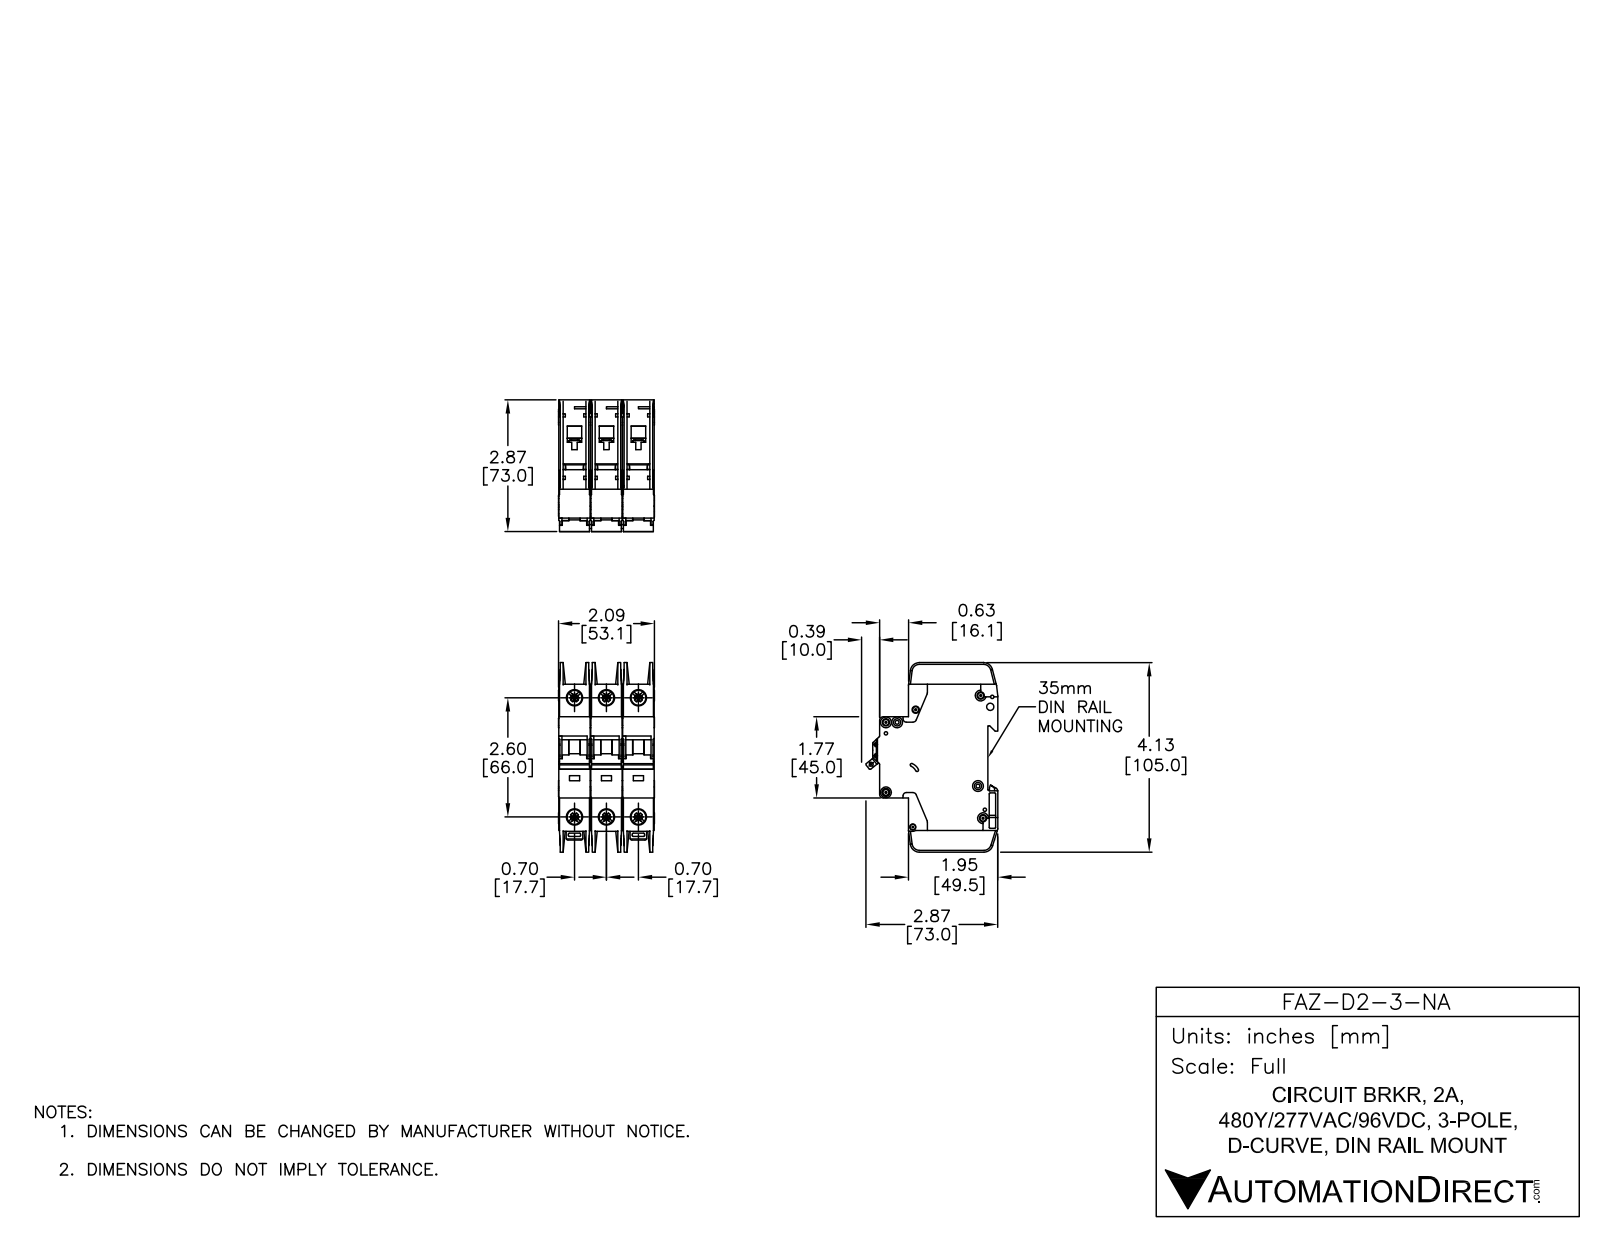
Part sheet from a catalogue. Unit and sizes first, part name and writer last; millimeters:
Units: millimetres
Overall size (bounding box): 105 × 73.04 × 53.1
Round holes (diameter × count): ⌀3.6 ×7, ⌀7.15 ×6, ⌀8.2 ×6, ⌀1.09 ×2, ⌀1.5 ×2, ⌀4 ×2, ⌀1.9 ×1, ⌀2.15 ×1, ⌀2.2 ×1, ⌀2.55 ×1, ⌀3.3 ×1, ⌀3.4 ×1
Round bosses / shafts (diameter × count): ⌀6 ×7, ⌀2.5 ×3
Partial cylindrical surfaces — rounded edges, fillets, slot ends (radius × count): R0.25 ×65, R0.5 ×30, R1 ×26, R2 ×14, R1.8 ×5, R5 ×5, R4 ×4, R0.2 ×2
Main face-to-face distances: 17.7, 35.4, 17.5, 35.2, 0.7, 15.05, 2.45, 1.75, 15.75, 13.3
Hole centre spacings: 17.7, 68.33, 66, 6.2, 35.4, 74.89, 5.19, 6.1
Volume: 233 085 mm³ · Surface area: 74 219 mm²
Bodies: 9 solids, 2352 faces (1227 planar, 789 cylindrical, 336 other)
Part name (STEP PRODUCT): FAZ-D2-3-NA
STEP written by: SolidWorks 2014 (AUTOMOTIVE_DESIGN)
